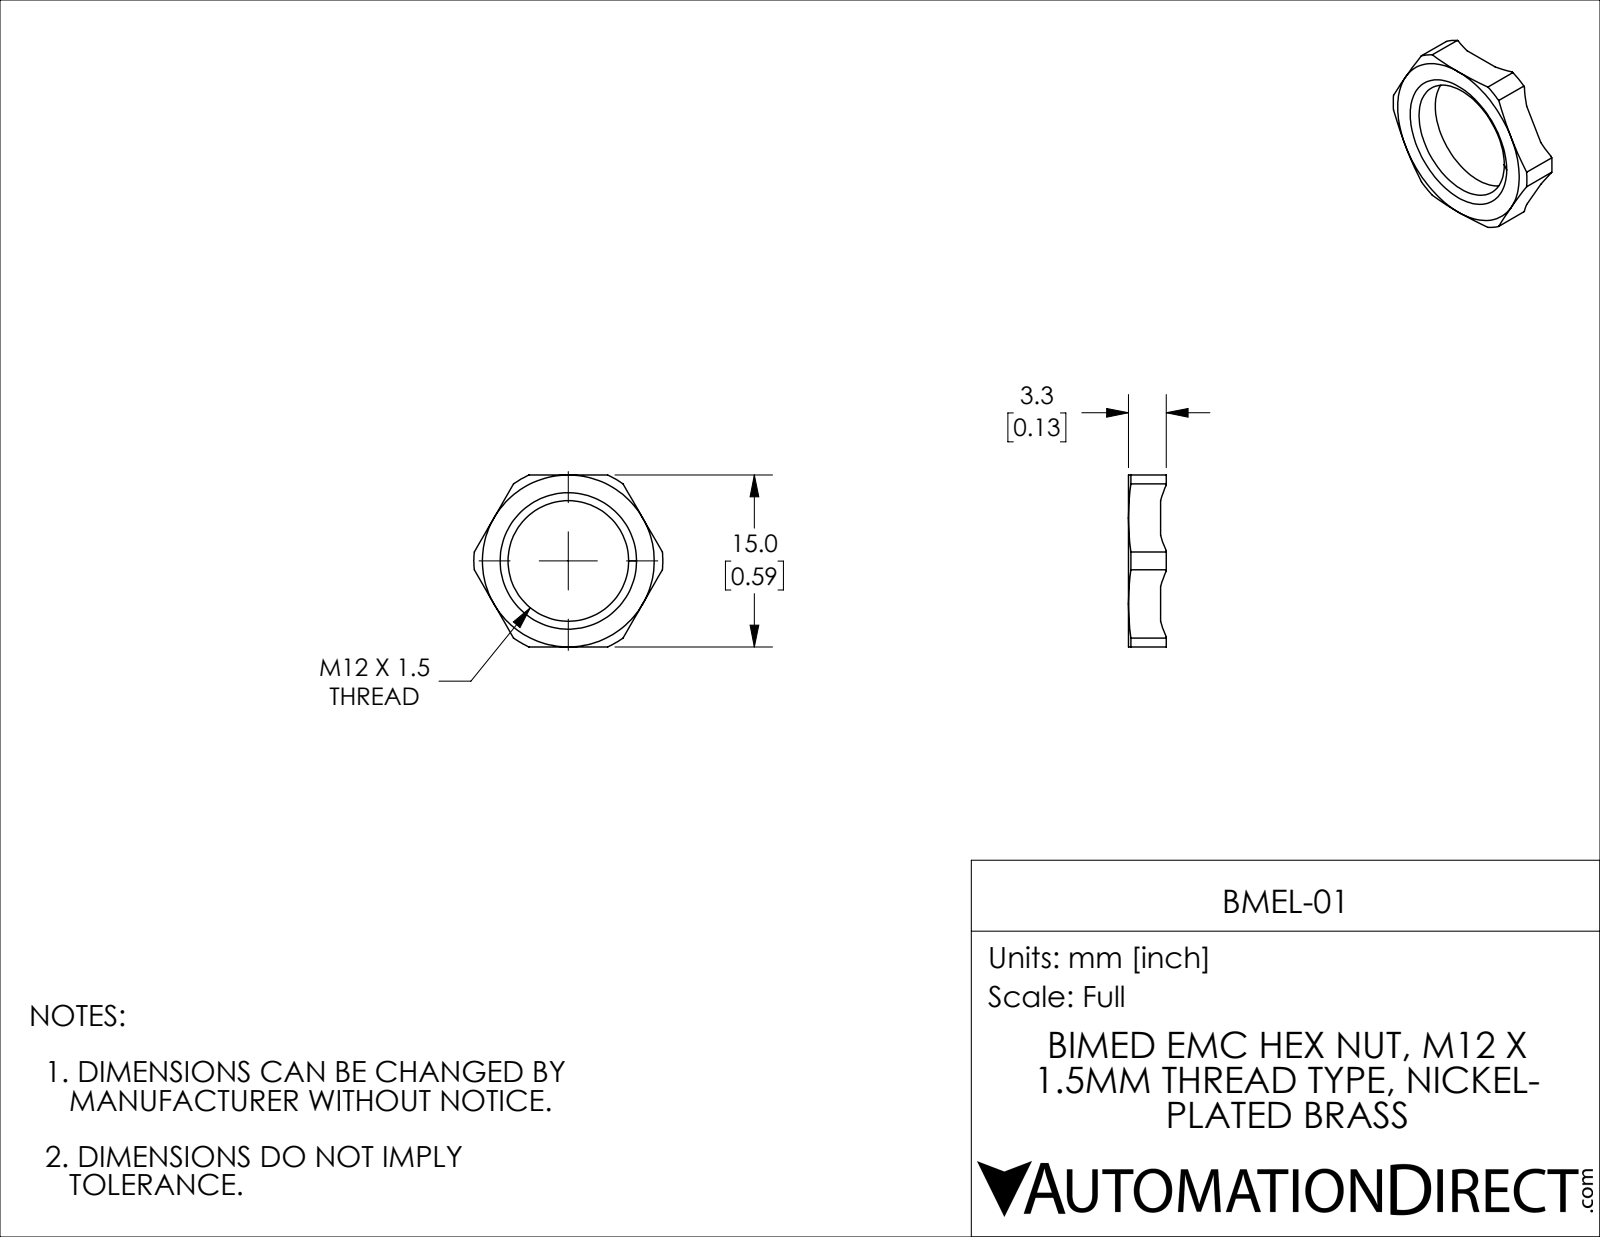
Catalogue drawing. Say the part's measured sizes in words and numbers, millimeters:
The part is named "BMEL-01". Its 3-D file was written by "SolidWorks 2021 (CONFIG_CONTROL_DESIGN)". It is 1 solid with 46 faces: 14 planar, 8 cylindrical and 24 other. Overall it measures 16.5 by 15 by 3.3 millimeters. Its volume is 288 cubic millimeters and its surface area 437 square millimeters. Round holes: 1 of diameter 10.53. Partial cylindrical surfaces (rounded edges, fillets, slot ends): 1 of radius 8.25. The main face-to-face distances are 2.8, 15, 0.5, 3.3.
